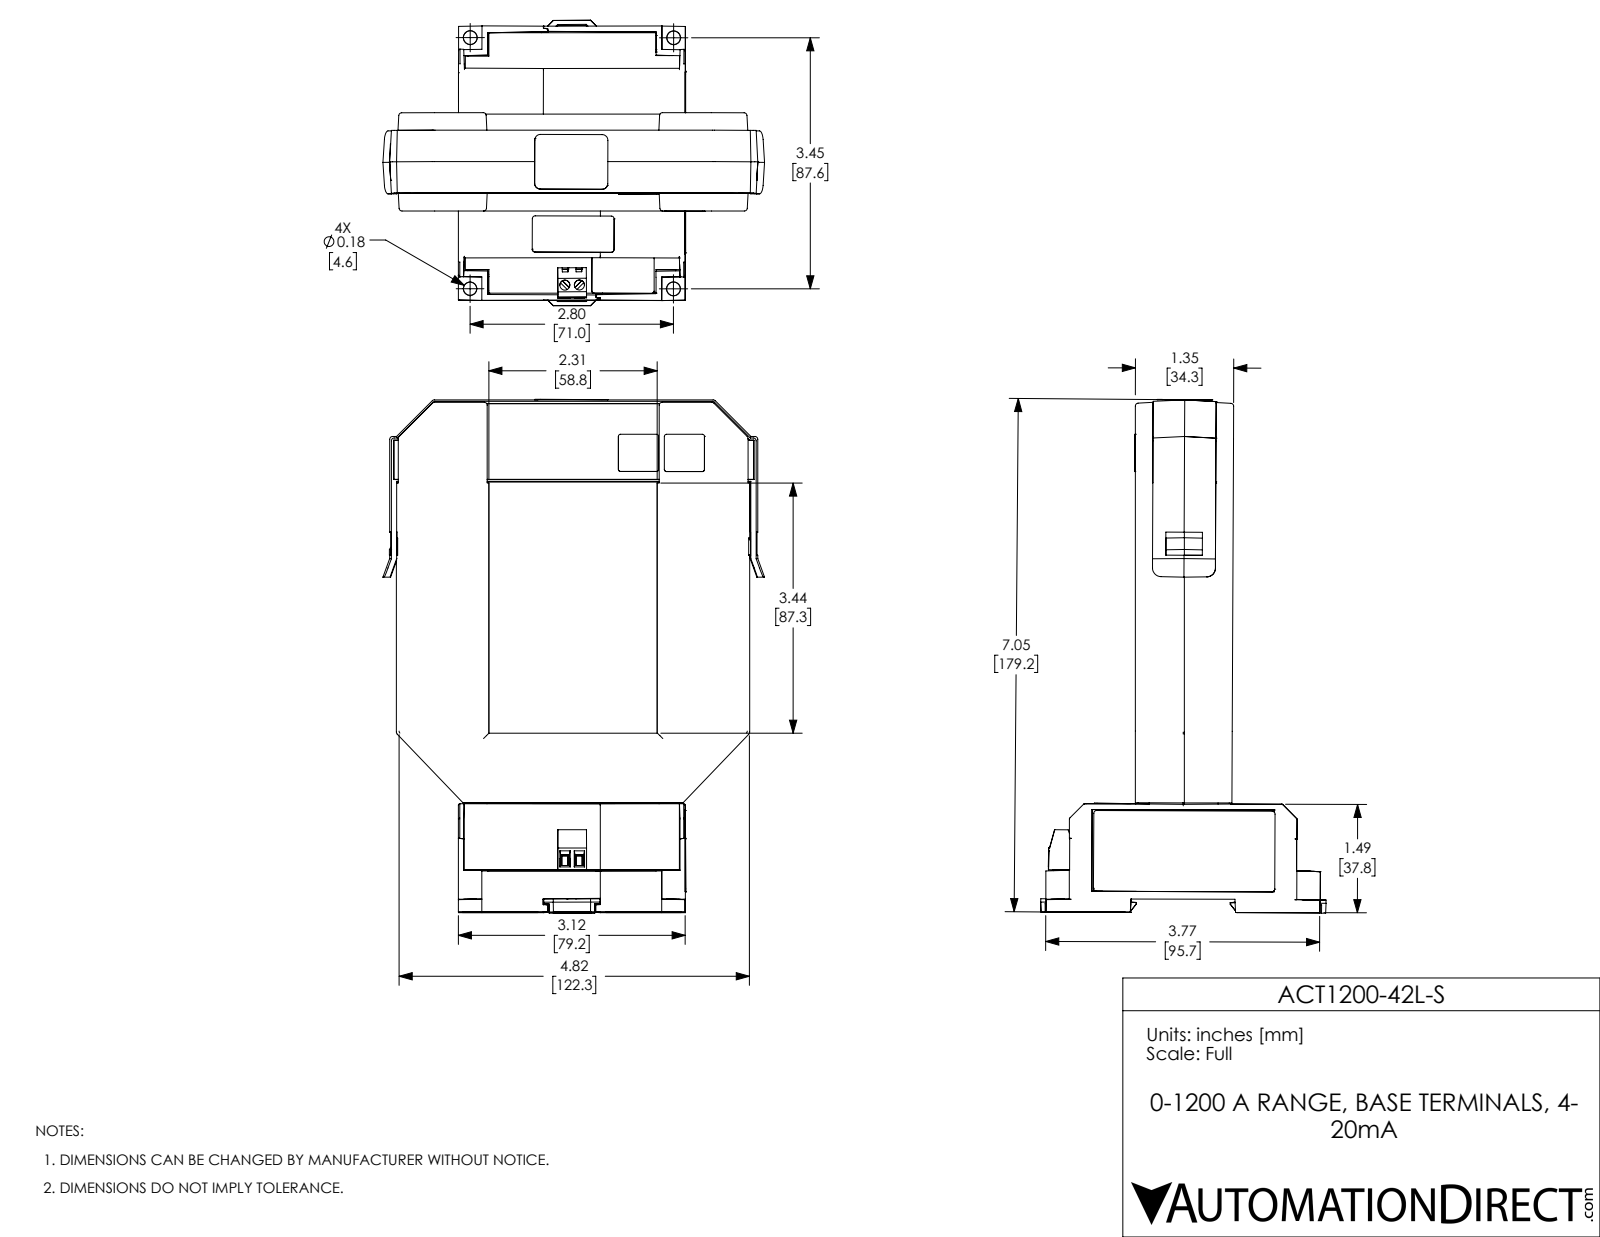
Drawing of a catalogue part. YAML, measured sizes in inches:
part_name: "ACT1200-42L-S"
step_written_by: "SolidWorks 2017 (AUTOMOTIVE_DESIGN)"
units: inches
bodies: {solids: 17, faces: 1436, planar: 1189, cylindrical: 167, other: 80}
overall_size: [7.061, 5.246, 3.923]
volume: 11.18
surface_area: 303.6
round_holes:
  - {diameter: 0.039, count: 4}
  - {diameter: 0.138, count: 2}
round_bosses_or_shafts:
  - {diameter: 0.197, count: 2}
  - {diameter: 0.118, count: 2}
partial_cylinders:
  - {radius: 0.04, count: 44}
  - {radius: 0.02, count: 30}
  - {radius: 0.03, count: 12}
  - {radius: 0.039, count: 12}
  - {radius: 0.004, count: 8}
  - {radius: 0.079, count: 4}
  - {radius: 0.129, count: 4}
  - {radius: 0.119, count: 2}
face_to_face_distances: [0.12, 0.059, 3.583, 0.08, 0.12, 0.239, 0.119, 3.028, 0.071, 0.904]
hole_center_spacings: [0.327, 0.547, 0.2, 0.22, 0.874]
